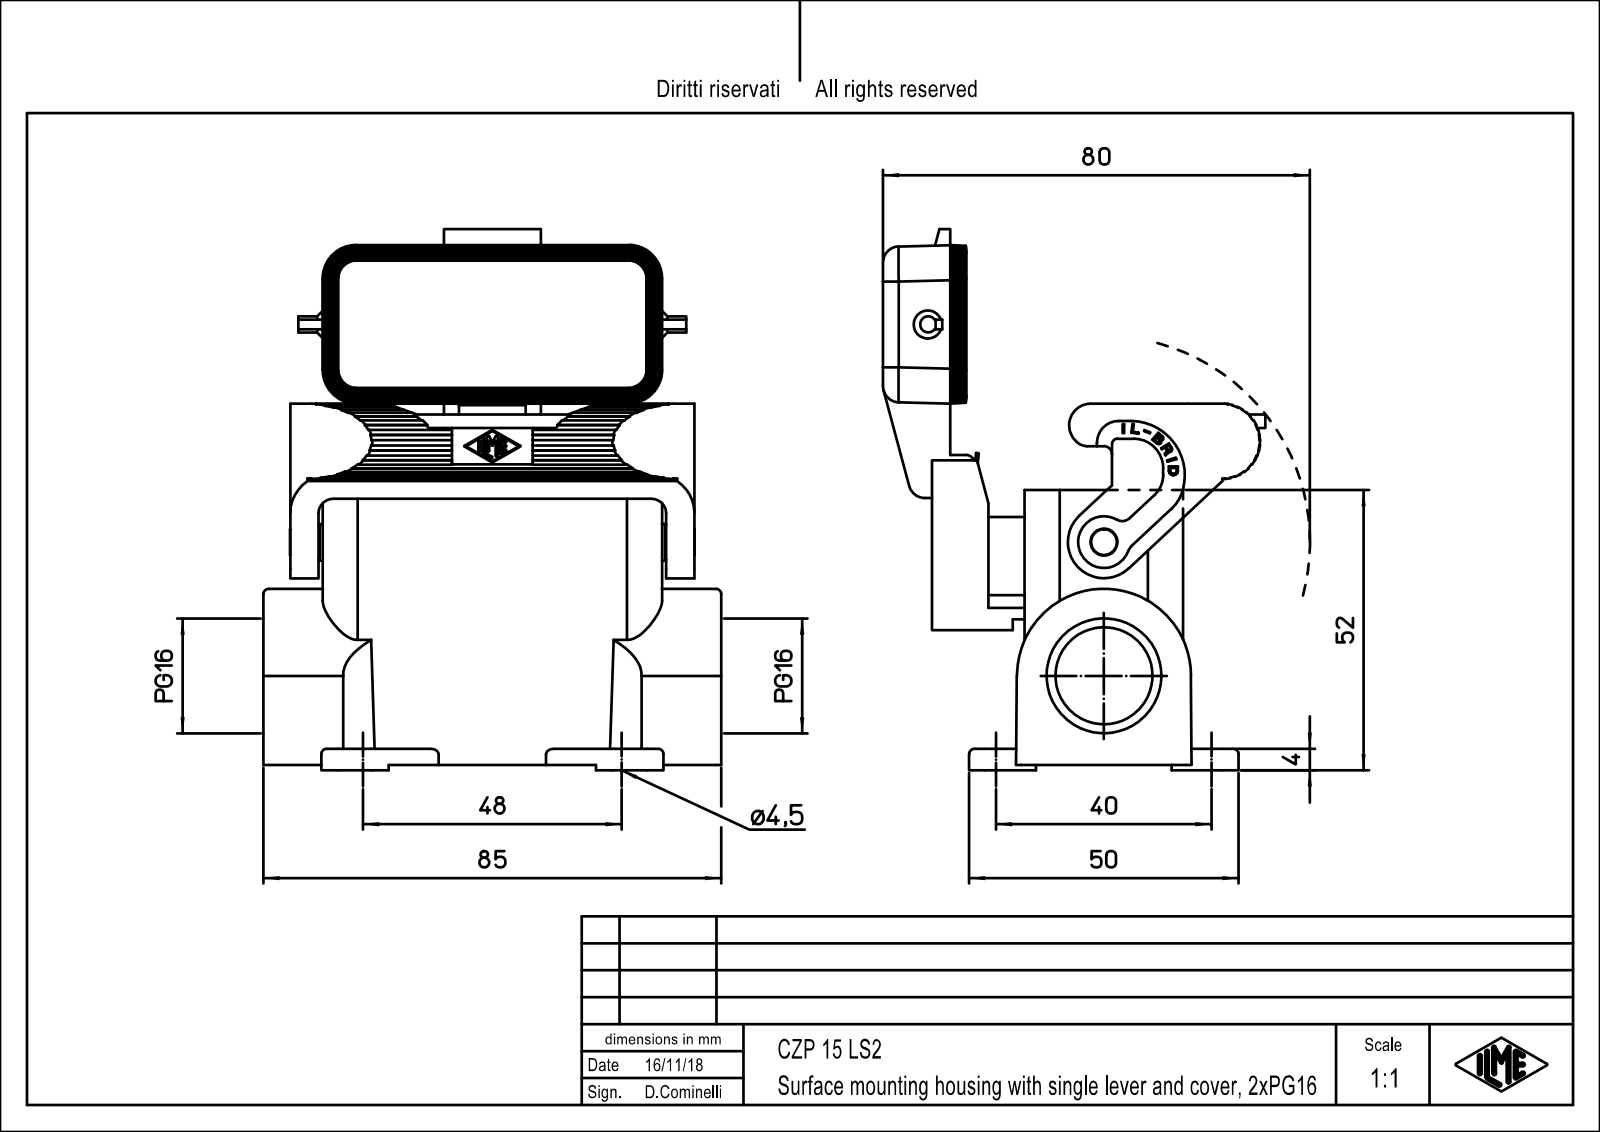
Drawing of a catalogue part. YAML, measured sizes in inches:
part_name: "CZP_15_LS2"
step_written_by: "PTC Creo Elements/Direct Modeling 19.0E 27-Jun-2016 (C) Parametric Technology GmbH (AUTOMOTIVE_DESIGN)"
units: inches
bodies: {solids: 1, faces: 538, planar: 307, cylindrical: 197, other: 34}
overall_size: [3.953, 3.346, 2.795]
volume: 4.847
surface_area: 73.12
round_holes:
  - {diameter: 0.118, count: 4}
  - {diameter: 0.177, count: 4}
  - {diameter: 0.197, count: 1}
  - {diameter: 0.709, count: 1}
  - {diameter: 0.839, count: 1}
round_bosses_or_shafts:
  - {diameter: 0.276, count: 1}
  - {diameter: 0.268, count: 1}
  - {diameter: 0.189, count: 1}
  - {diameter: 0.118, count: 1}
partial_cylinders:
  - {radius: 0.008, count: 15}
  - {radius: 0.118, count: 14}
  - {radius: 0.039, count: 13}
  - {radius: 0.256, count: 8}
  - {radius: 0.138, count: 4}
  - {radius: 0.138, count: 4}
  - {radius: 0.236, count: 4}
  - {radius: 0.004, count: 3}
face_to_face_distances: [0.102, 1.055, 0.953, 1.157, 2.264, 0.079, 0.118, 1.059, 2.114, 2.012]
hole_center_spacings: [0.473, 1.103, 1.977, 2.213, 0.63, 1.575, 1.89, 1.949]
